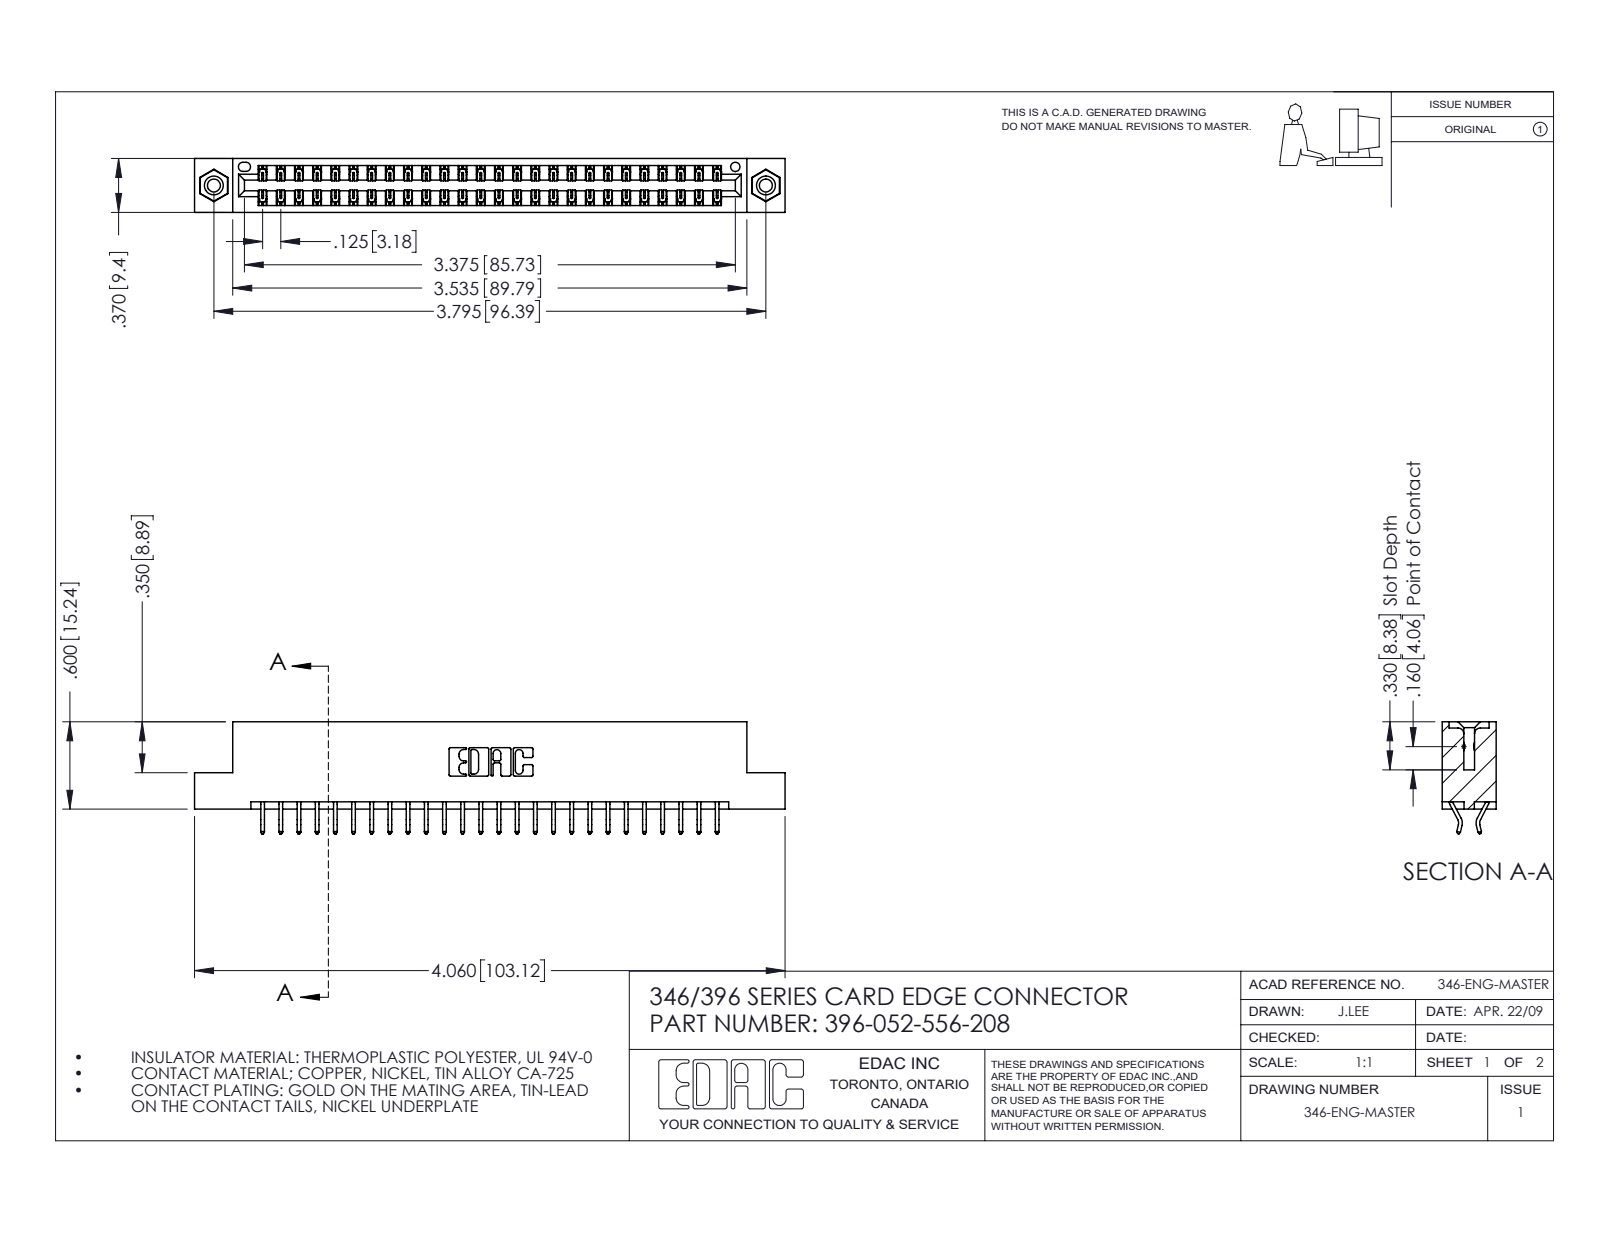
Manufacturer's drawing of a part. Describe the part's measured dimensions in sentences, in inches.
The part is named "345-292-001_556 Tail; 346 Part_Flush Mounting Lugs - 0.156 Dia-TI; 345-250-001_345-250-003-102; 396-052-556-208". Its 3-D file was written by "SolidWorks 2016 (CONFIG_CONTROL_DESIGN)". It is 55 solids with 3198 faces: 2136 planar, 1046 cylindrical and 16 other. Overall it measures 4.06 by 0.77 by 0.37 inches. Its volume is 0.606 cubic inches and its surface area 20.71 square inches. Round holes: 2 of diameter 0.089, 2 of diameter 0.125, 2 of diameter 0.156, 1 of diameter 0.064. Round bosses or shafts: 2 of diameter 0.155. Partial cylindrical surfaces (rounded edges, fillets, slot ends): 78 of radius 0.006, 22 of radius 0.01, 6 of radius 0.007, 6 of radius 0.031, 3 of radius 0.026, 2 of radius 0.01, 2 of radius 0.014, 2 of radius 0.022. The main face-to-face distances are 0.048, 0.322, 0.37, 0.25, 0.025, 0.072, 0.298, 0.275, 0.148, 0.222. The hole center spacings are 0.246, 3.587, 3.795.
